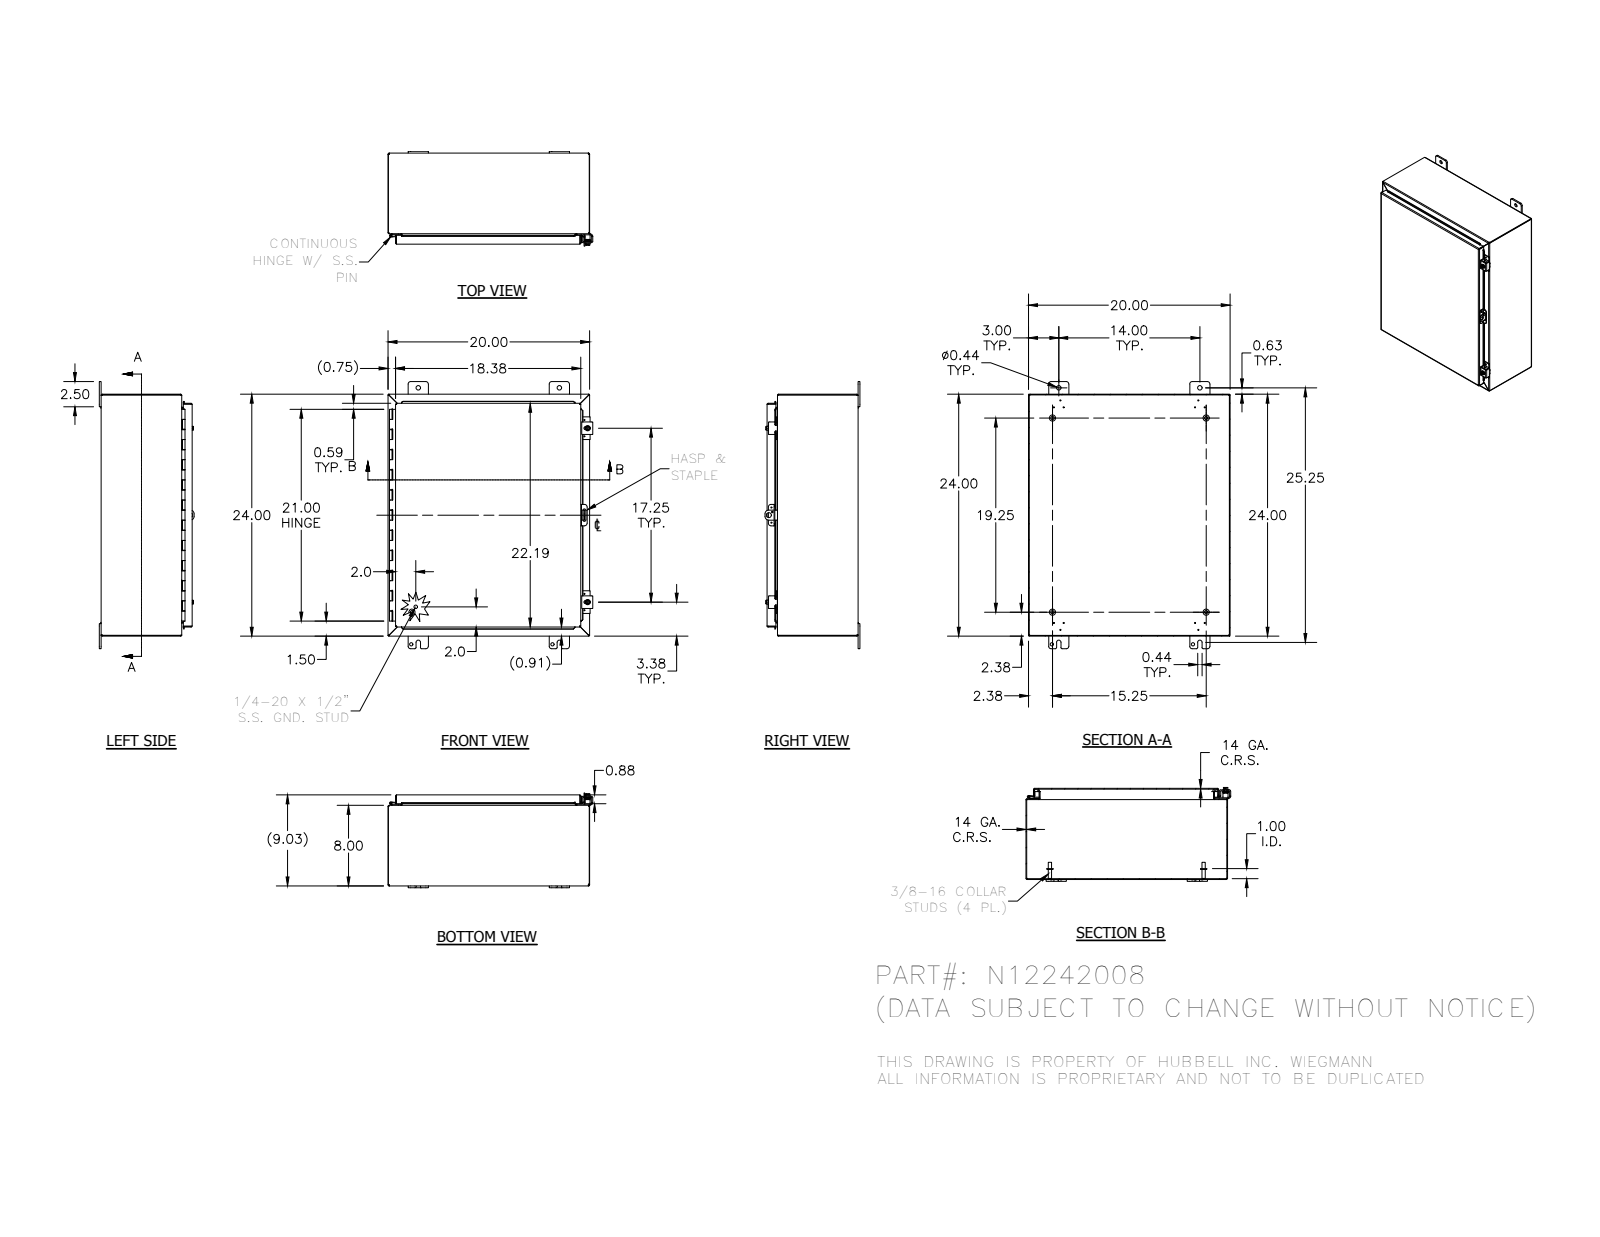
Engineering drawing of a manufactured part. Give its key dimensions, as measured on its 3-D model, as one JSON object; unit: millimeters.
{"part_name": "N12242008; 34840; 38420; N12242008BKP (+8 more)", "step_written_by": "Autodesk Inventor 2012 (AUTOMOTIVE_DESIGN)", "units": "millimeters", "bodies": {"solids": 27, "faces": 982, "planar": 533, "cylindrical": 332, "other": 117}, "overall_size": [673.1, 515.9, 239], "volume_mm3": 2496000, "surface_area_mm2": 2564000, "round_holes": [[3, 12], [2.8, 7], [8, 4], [11.1, 4], [5.4, 2], [7.1, 2], [7.6, 2], [3.2, 1], [4, 1], [12.7, 1]], "round_bosses_or_shafts": [[15.9, 4], [8.4, 4], [6.4, 4], [13.2, 2], [12.7, 2], [8.9, 2], [2.9, 2], [8.6, 1]], "partial_cylinders_radius": [[0.8, 27], [1.6, 25], [3.2, 25], [6.4, 25], [0.8, 23], [2.7, 23], [1.8, 8], [2.5, 4]], "face_to_face_distances": [1.9, 227.6, 225.7, 229.4, 506.1, 607.7, 201.3, 26.2, 508, 504.2], "hole_center_spacings": [355.6, 19.3, 21.3, 23.9, 24.6, 339.7, 364.3, 543.1]}
